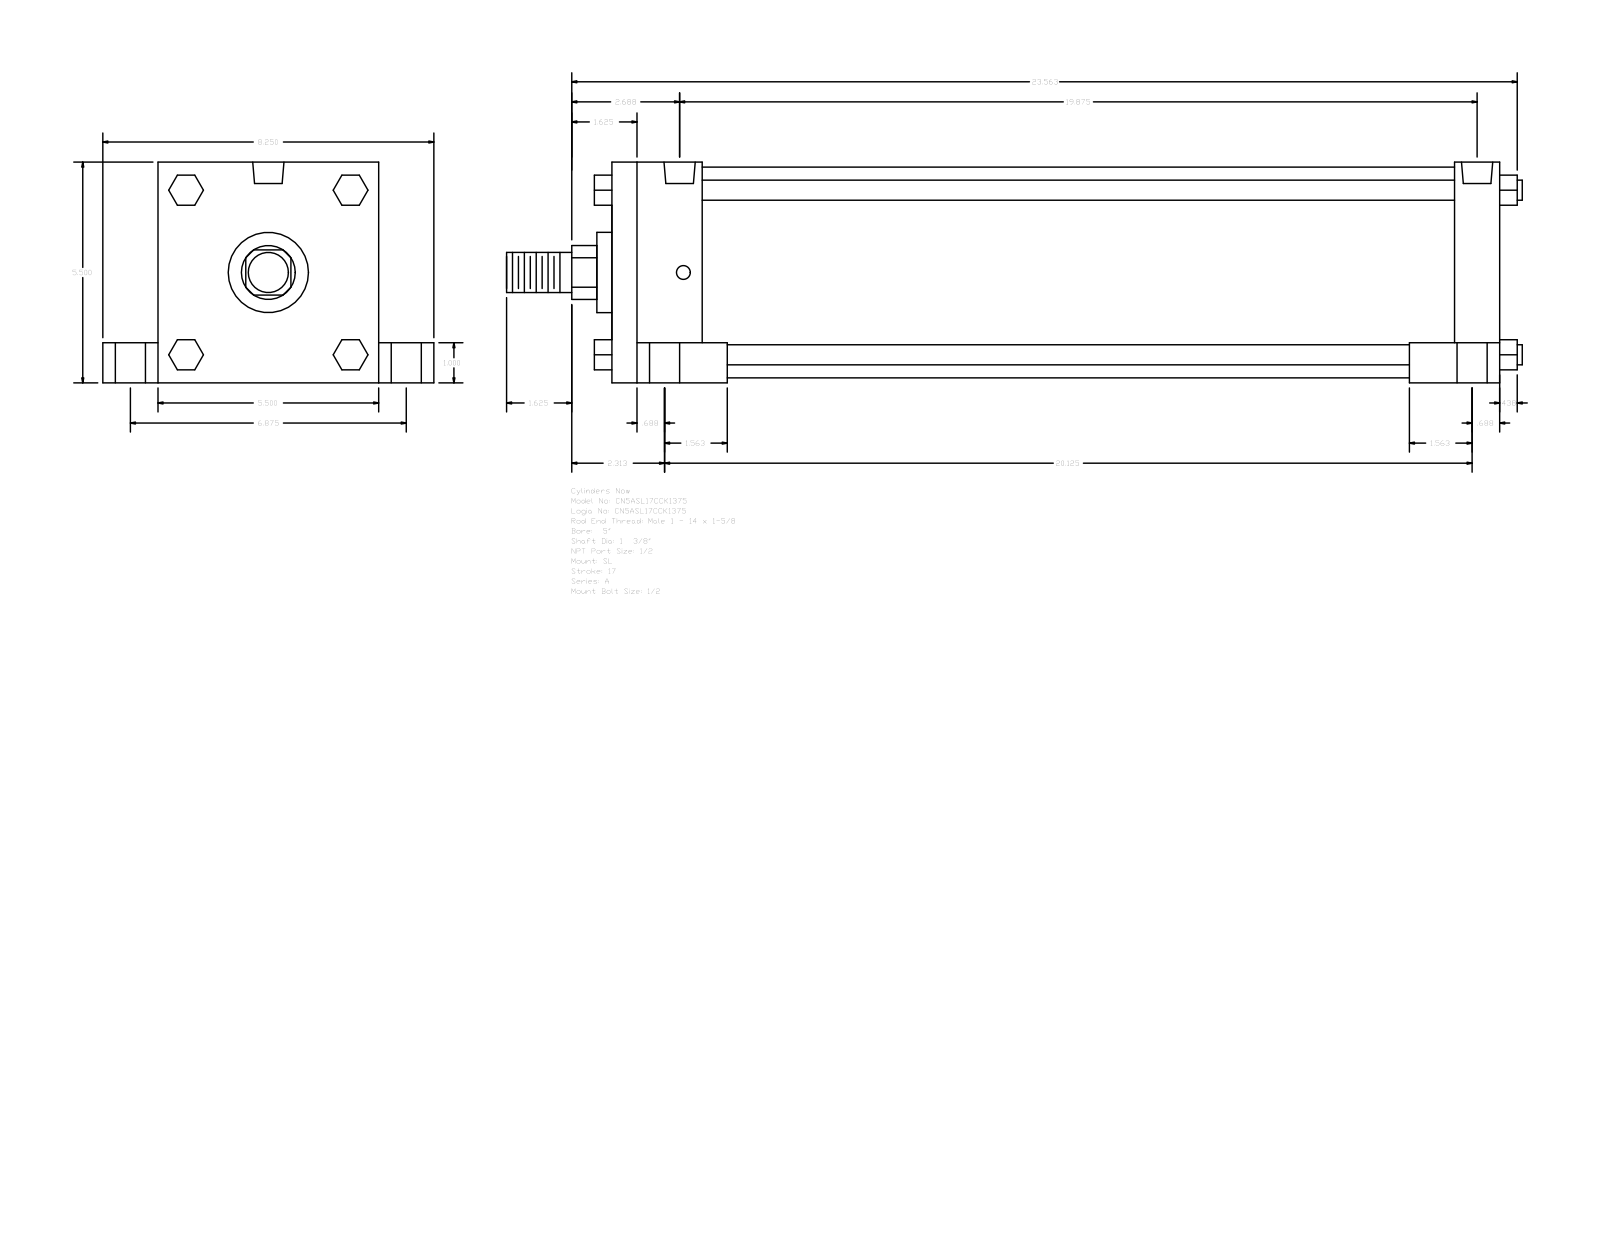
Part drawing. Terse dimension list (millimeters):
name: A_SL__0500_1.375
written by: GSSL Pune (CONFIG_CONTROL_DESIGN)
unit: mm
bodies: 0 solids, 150 faces (114 planar, 36 cylindrical, 0 other)
size: 642.94 × 209.55 × 139.7
holes: 4× ⌀8.73, 4× ⌀19.05, 4× ⌀25.4, 2× ⌀19.77
bosses: 4× ⌀12.7, 1× ⌀133.35, 1× ⌀50.8, 1× ⌀34.92, 1× ⌀25.4
rounds: 1× R17.06
face distances: 139.7, 561.98, 57.15, 504.83, 25.4, 114.3, 34.93, 174.63, 28.58, 533.4
hole spacings: 2.39, 87.31, 87.37, 87.83, 88.12, 174.62, 500.05, 502.44
